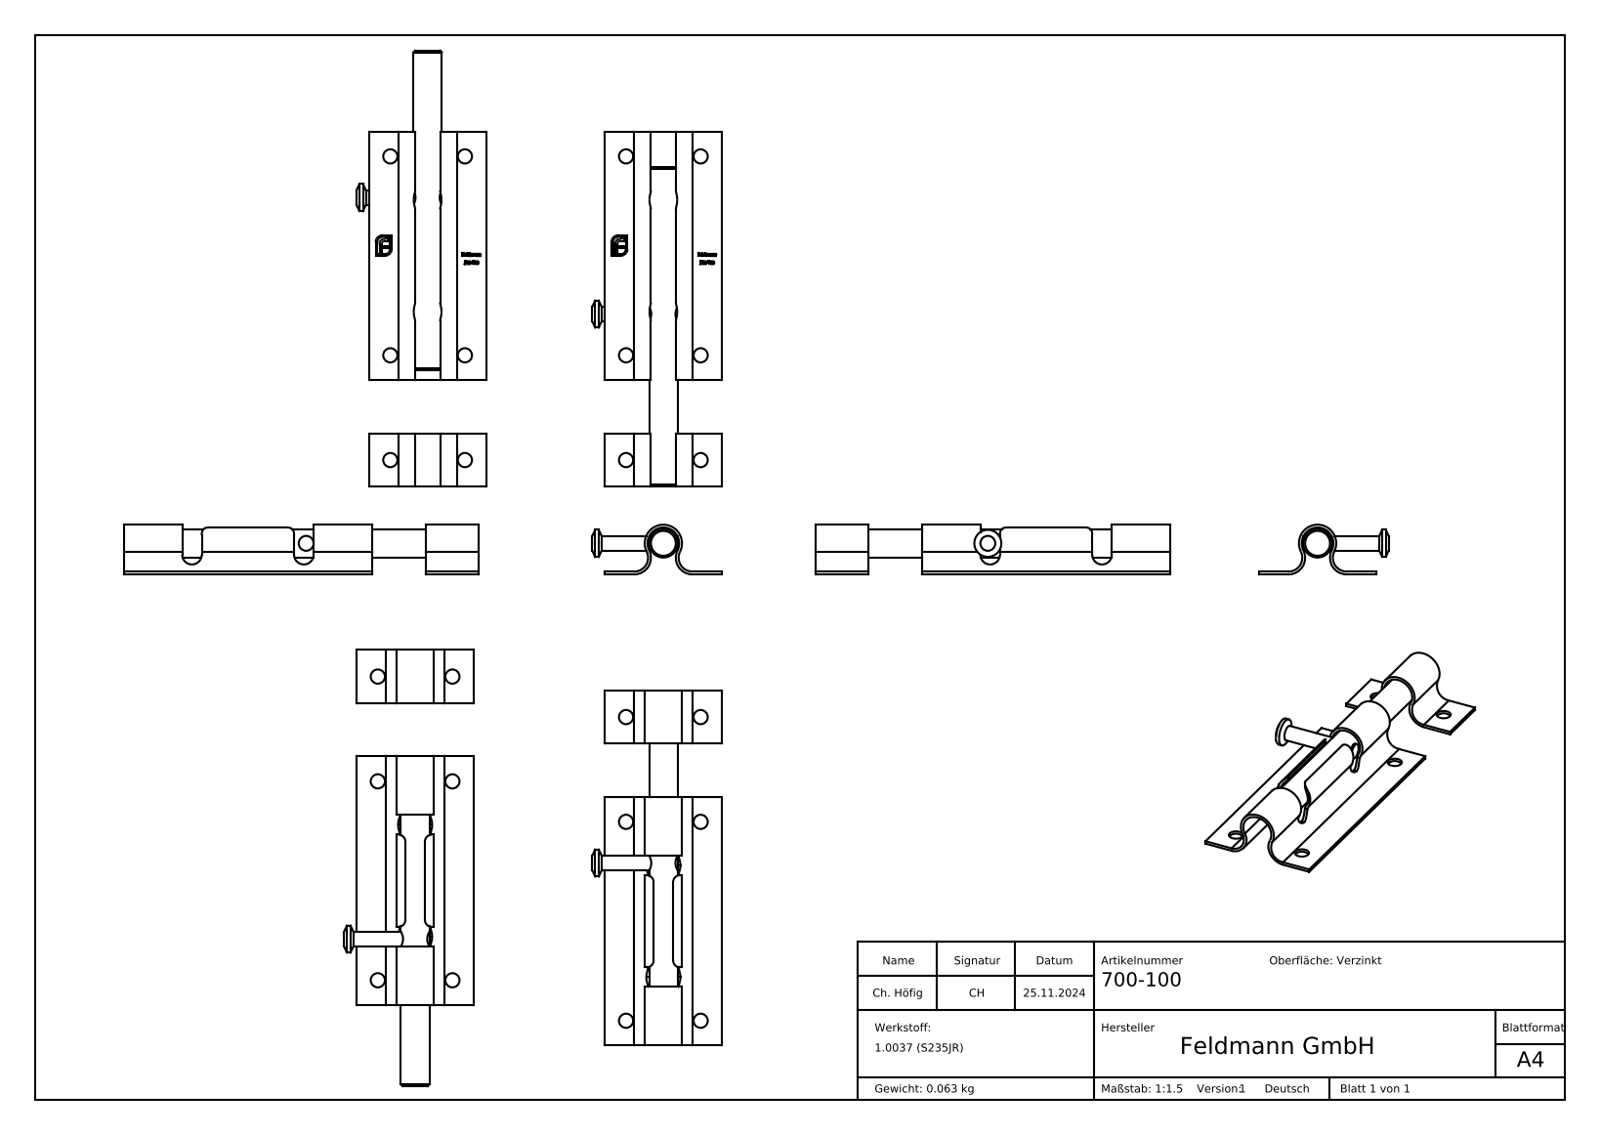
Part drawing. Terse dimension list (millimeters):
name: 700-XXX Teil2_700-100 Teil2; 700-XXX Teil3_700-XXX Teil3; 700-XXX Teil1_700-100 Teil1; 700-100
written by: SolidWorks 2018 (CONFIG_CONTROL_DESIGN)
unit: mm
bodies: 4 solids, 289 faces (141 planar, 40 cylindrical, 108 other)
size: 100 × 36.5 × 14
volume: 8 034 mm³; area: 11 428 mm²
holes: 6× ⌀4, 1× ⌀4.2
bosses: 1× ⌀8, 1× ⌀7.6
rounds: 4× R2, 2× R2.75, 2× R3.89, 2× R4.69, 1× R4.45, 1× R5.25
face distances: 0.8, 15, 33, 100, 85, 30, 70, 13.75, 19.25, 90
hole spacings: 21, 29.5, 36.21, 56, 59.81, 85.5, 88.04
